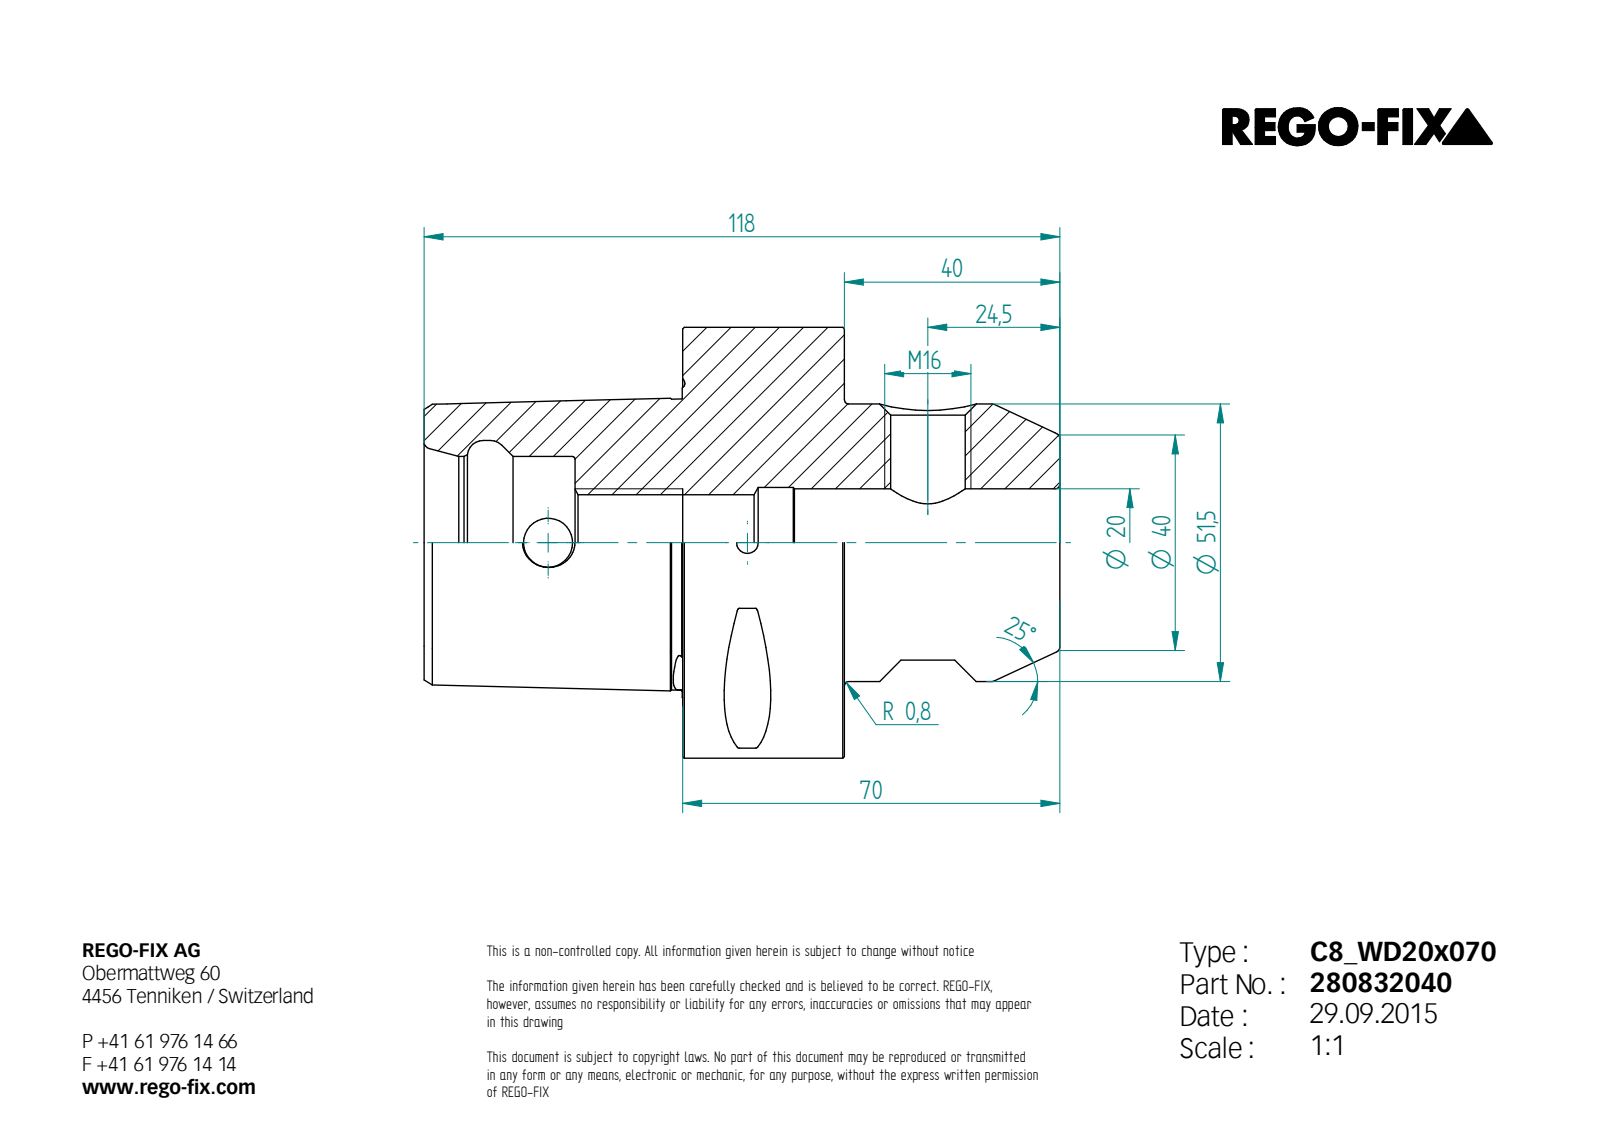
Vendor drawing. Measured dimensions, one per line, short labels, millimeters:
written by: Unknown (AUTOMOTIVE_DESIGN)
unit: mm
bodies: 1 solid, 104 faces (23 planar, 21 cylindrical, 60 other)
size: 118 × 80 × 80
volume: 277 158 mm³; area: 40 113 mm²
holes: 1× ⌀4, 1× ⌀9.1, 1× ⌀13.84, 1× ⌀17.84, 1× ⌀20, 1× ⌀20.5, 1× ⌀32, 1× ⌀38
bosses: 1× ⌀80, 1× ⌀51.5
rounds: 8× R0.5
face distances: 30, 48, 78, 118, 70, 40, 32.55, 28, 20, 50
hole spacings: 37
